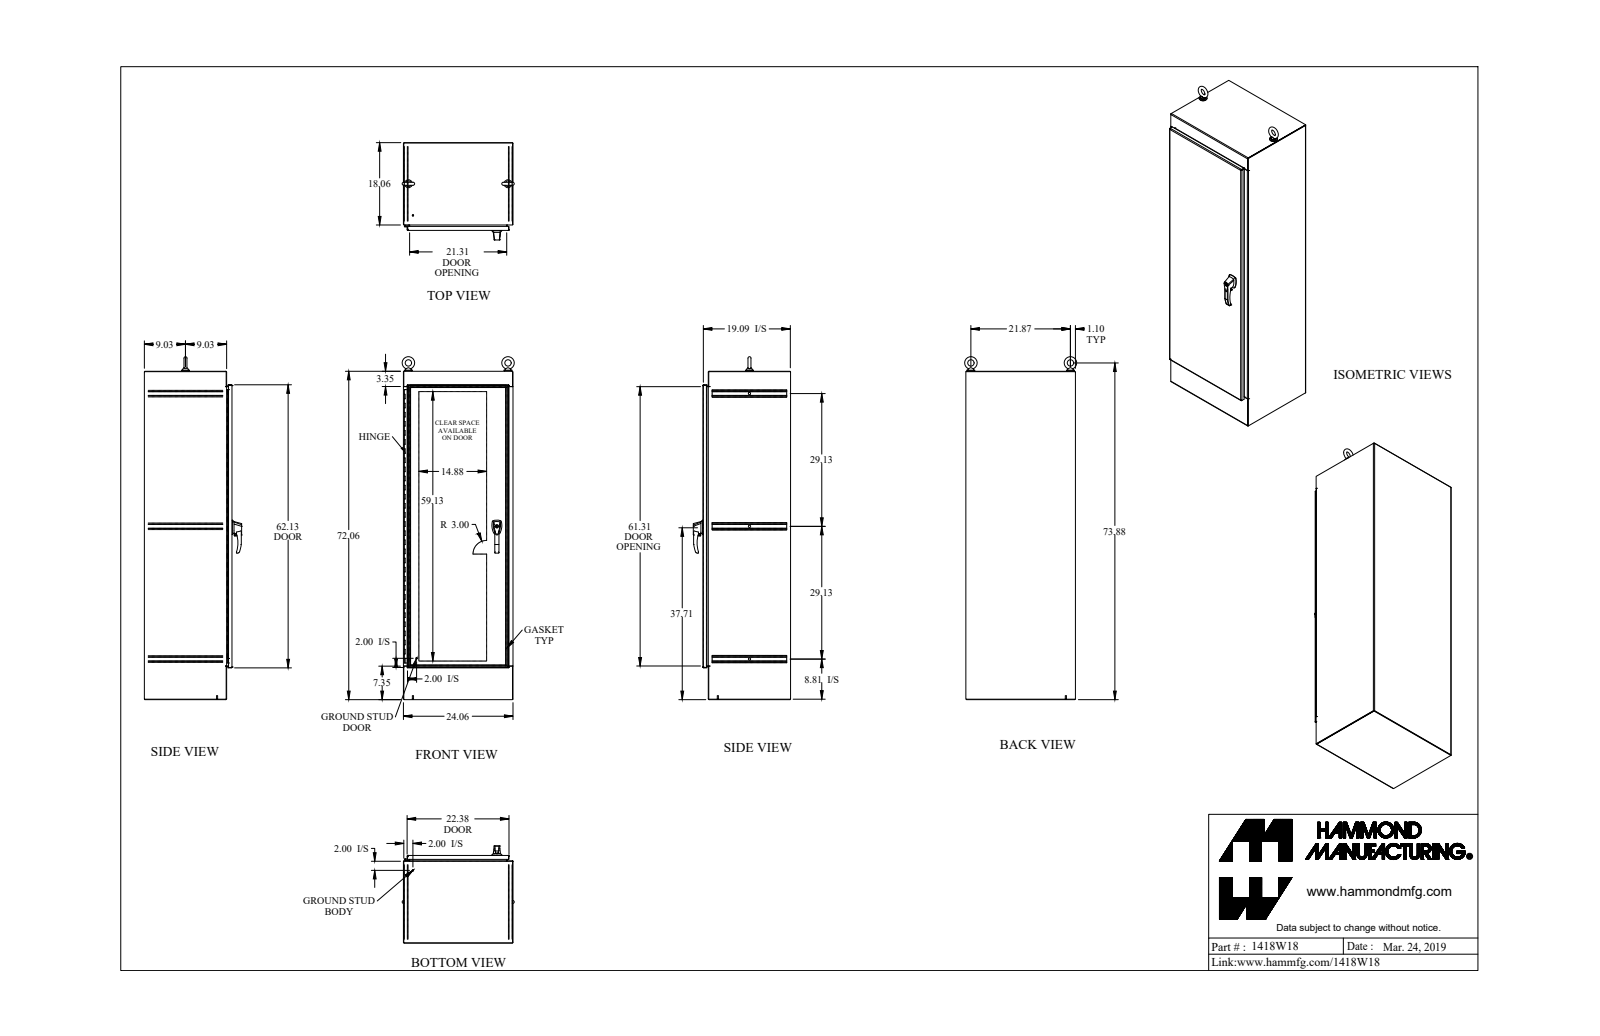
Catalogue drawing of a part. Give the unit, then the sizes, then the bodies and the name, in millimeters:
Units: millimetres
Overall size (bounding box): 1923.1 × 638 × 542.6
Round holes (diameter × count): ⌀7.7 ×10, ⌀19.1 ×4, ⌀12.7 ×3, ⌀6.4 ×2, ⌀6.5 ×2, ⌀7.1 ×2, ⌀7.1 ×2, ⌀8 ×2, ⌀9.9 ×2, ⌀10.5 ×2, ⌀13.4 ×2, ⌀15.9 ×2
Round bosses / shafts (diameter × count): ⌀7.1 ×4, ⌀44.5 ×2, ⌀38.1 ×2, ⌀31.8 ×2, ⌀25.4 ×2, ⌀19.1 ×2, ⌀18.7 ×2, ⌀16 ×2
Partial cylindrical surfaces — rounded edges, fillets, slot ends (radius × count): R1.1 ×42, R3.5 ×36, R3.2 ×22, R0.5 ×16, R1.2 ×14, R3.6 ×14, R1.5 ×10, R8.1 ×7
Main face-to-face distances: 2.4, 608.7, 2.4, 484, 486.5, 606.3, 486.5, 488.9, 611.1, 1827.9
Hole centre spacings: 152.4, 304.8, 457.2, 609.6, 762, 555.5, 914.4, 1066.8
Volume: 13 130 000 mm³ · Surface area: 10 880 000 mm²
Bodies: 52 solids, 1742 faces (781 planar, 796 cylindrical, 165 other)
Part name (STEP PRODUCT): 1418W18_Default
STEP written by: SolidWorks 2019 (CONFIG_CONTROL_DESIGN)
